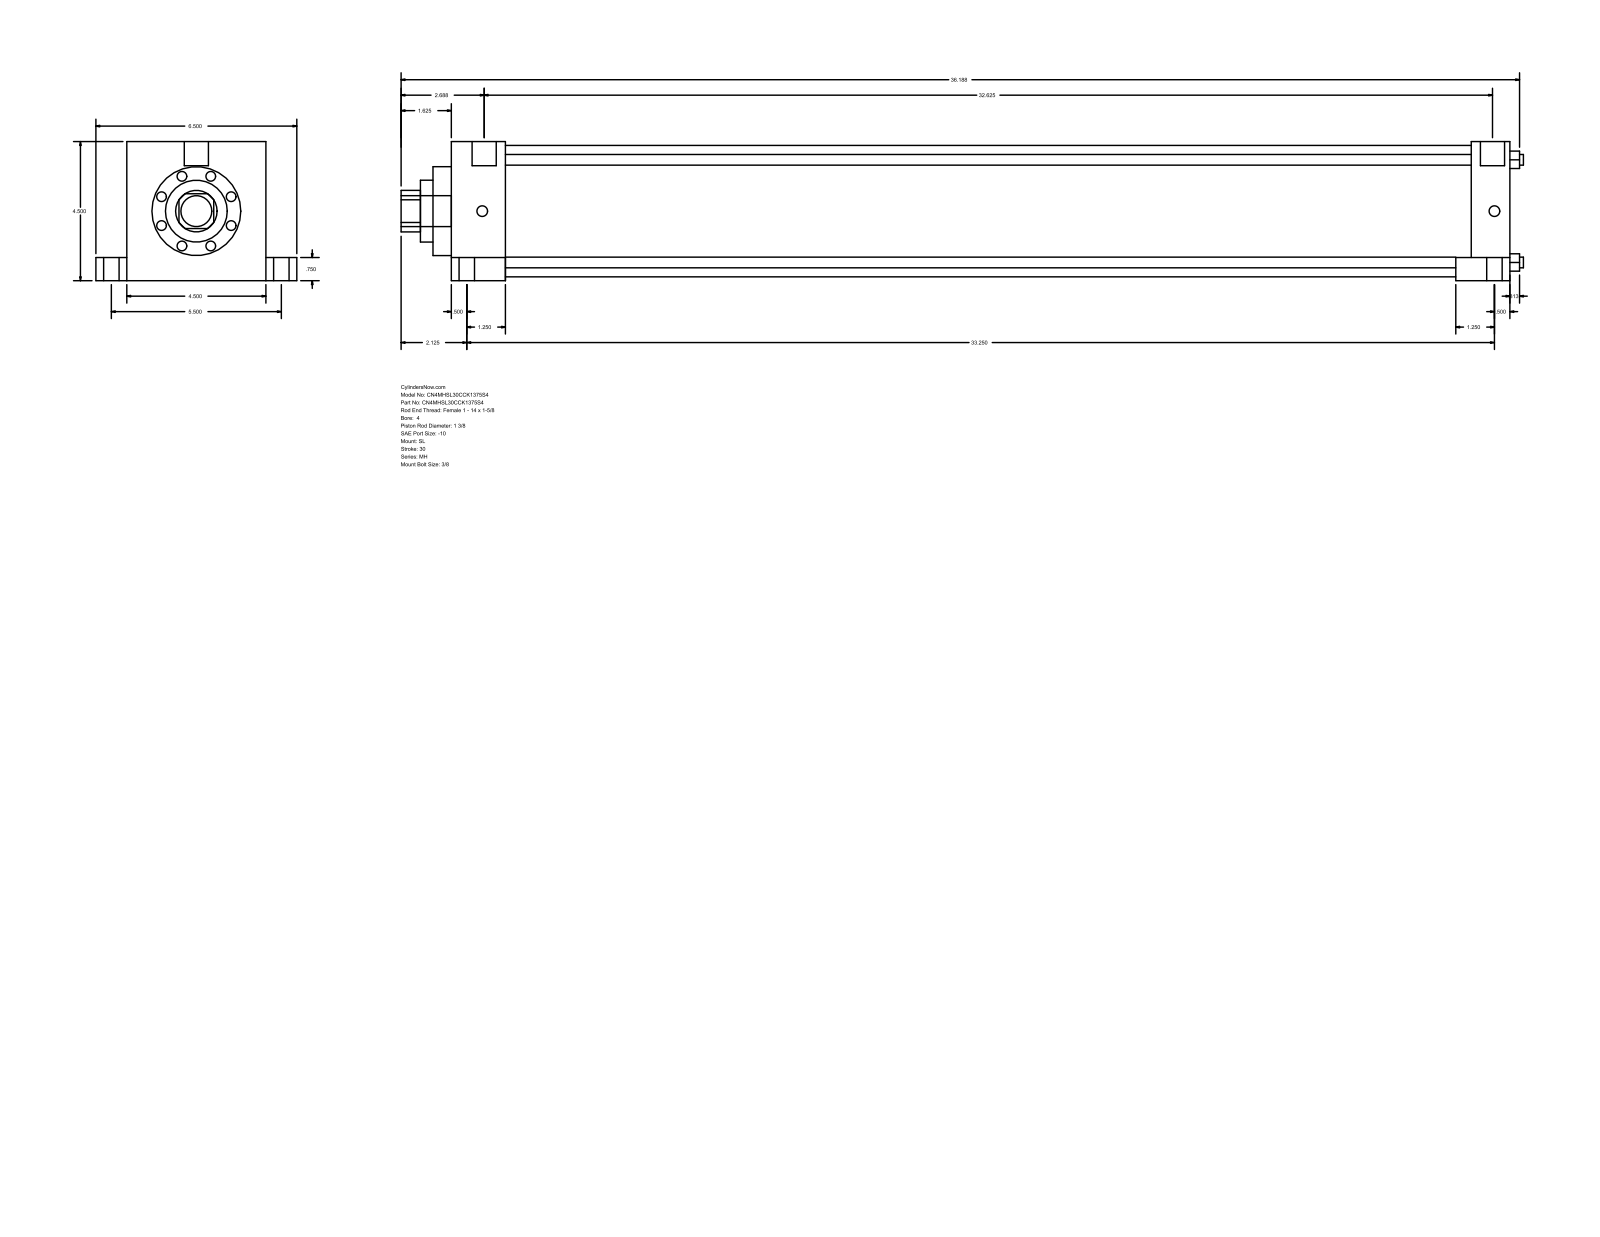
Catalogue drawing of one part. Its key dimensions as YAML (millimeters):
part_name: "MH_SL__0400_1.375"
step_written_by: "GSSL Pune (CONFIG_CONTROL_DESIGN)"
units: millimeters
bodies: {solids: 0, faces: 110, planar: 77, cylindrical: 33, other: 0}
overall_size: [922.34, 165.1, 114.3]
round_holes:
  - {diameter: 8.76, count: 4}
  - {diameter: 34.92, count: 1}
  - {diameter: 50.8, count: 1}
  - {diameter: 73.03, count: 1}
  - {diameter: 107.95, count: 1}
round_bosses_or_shafts:
  - {diameter: 19.05, count: 4}
  - {diameter: 12.7, count: 4}
  - {diameter: 8.73, count: 4}
  - {diameter: 19.84, count: 2}
  - {diameter: 25.4, count: 1}
partial_cylinders:
  - {radius: 17.06, count: 1}
face_to_face_distances: [114.3, 869.96, 44.45, 825.51, 838.21, 793.76, 31.75, 25.4, 139.7, 19.05]
hole_center_spacings: [59.62, 84.32, 119.25]
